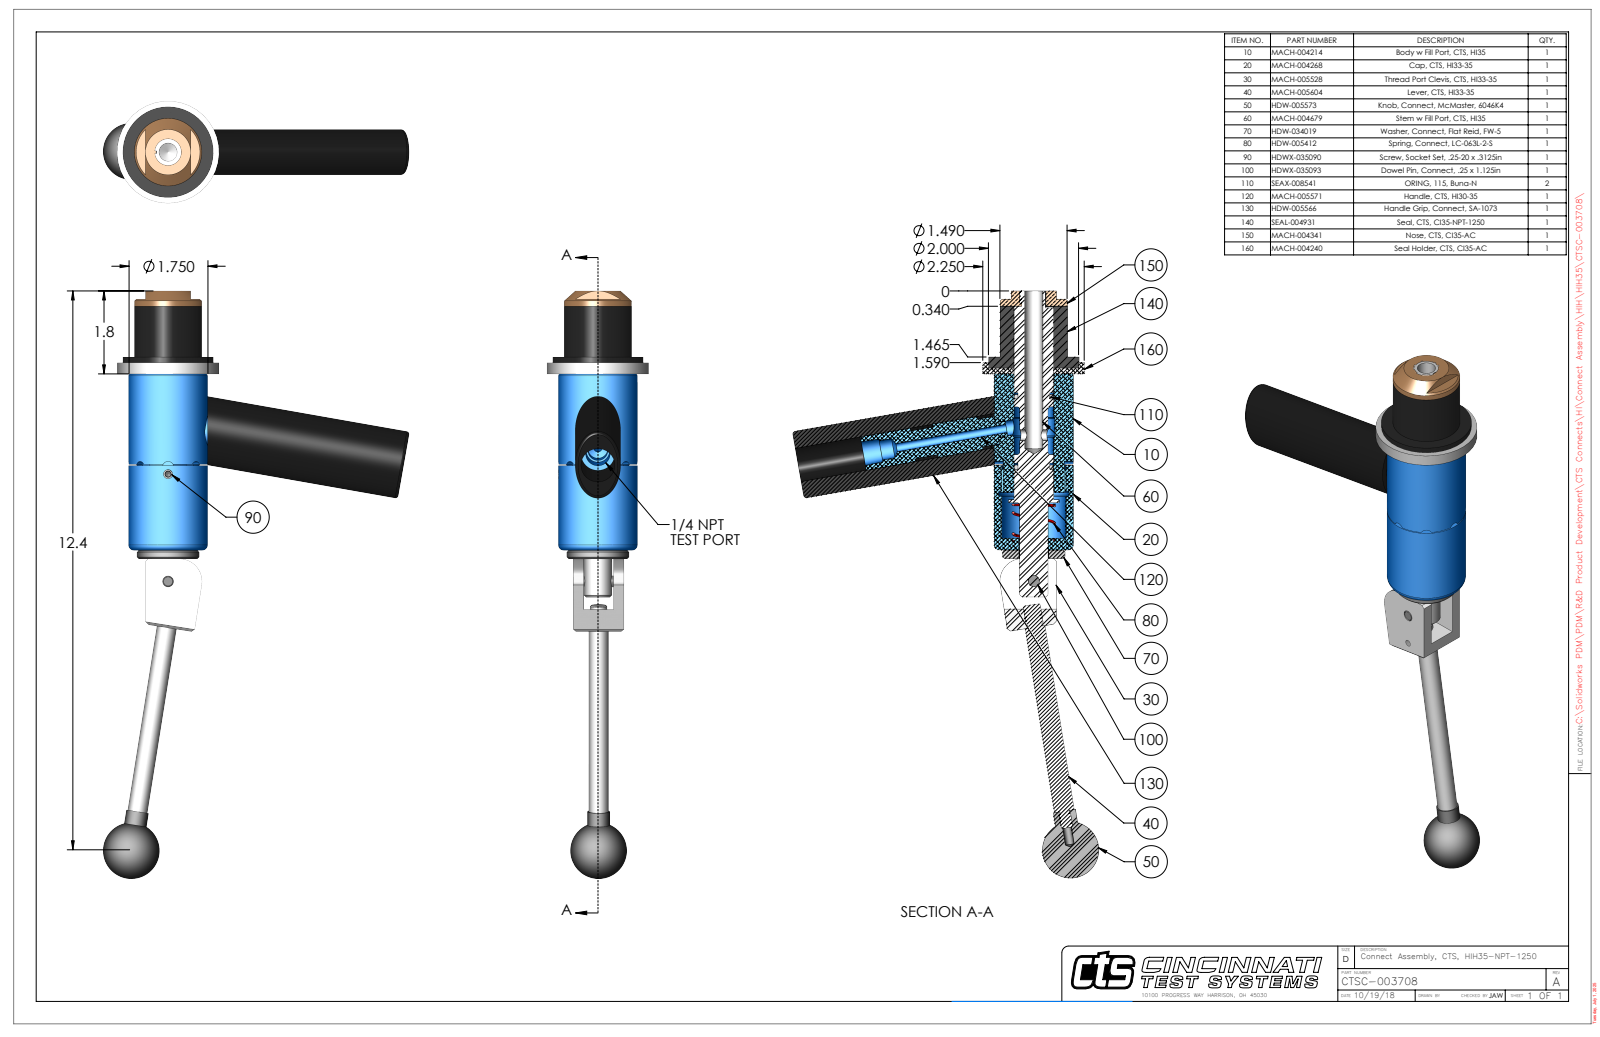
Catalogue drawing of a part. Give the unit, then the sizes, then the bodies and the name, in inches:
Units: inches
Overall size (bounding box): 13.02 × 6.763 × 2.25
Round holes (diameter × count): ⌀0.201 ×2, ⌀0.15 ×1, ⌀0.187 ×1, ⌀0.249 ×1, ⌀0.25 ×1, ⌀0.251 ×1, ⌀0.313 ×1, ⌀0.406 ×1, ⌀0.438 ×1, ⌀0.531 ×1, ⌀0.635 ×1, ⌀0.656 ×1
Round bosses / shafts (diameter × count): ⌀0.25 ×2, ⌀2.25 ×1, ⌀2 ×1, ⌀1.75 ×1, ⌀1.49 ×1, ⌀1.38 ×1, ⌀0.869 ×1, ⌀0.75 ×1
Partial cylindrical surfaces — rounded edges, fillets, slot ends (radius × count): R0.125 ×4, R0.029 ×2, R0.166 ×1, R0.166 ×1, R0.247 ×1, R0.33 ×1, R0.5 ×1, R0.695 ×1
Main face-to-face distances: 0.125, 1.5, 1.375, 5.405, 4.03, 3.905, 0.25, 1.12, 0.375, 1.125
Hole centre spacings: 0.74, 2.376, 3.116
Volume: 20.34 in³ · Surface area: 138.1 in²
Bodies: 11 solids, 302 faces (108 planar, 129 cylindrical, 65 other)
Part name (STEP PRODUCT): CTSC-003708
STEP written by: SolidWorks 2023 (AUTOMOTIVE_DESIGN)
